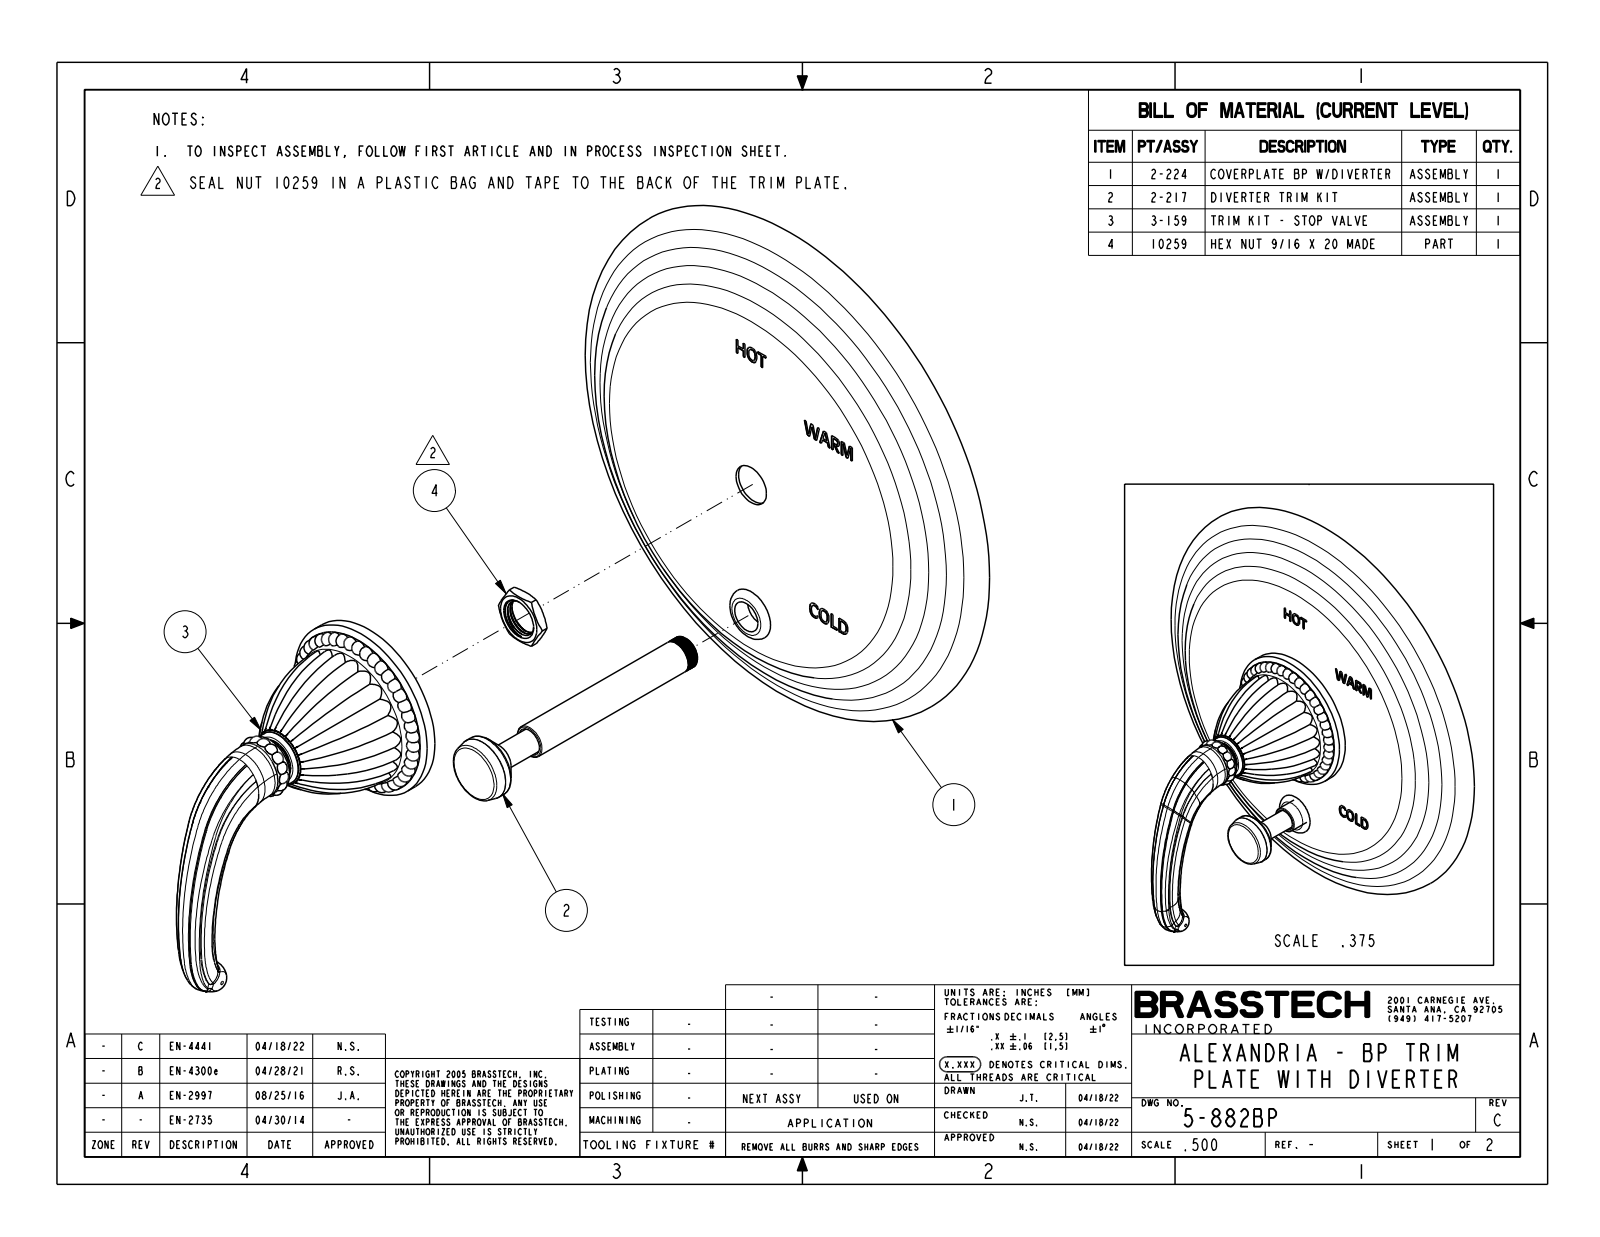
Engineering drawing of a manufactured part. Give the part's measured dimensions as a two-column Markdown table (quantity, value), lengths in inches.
| quantity | value |
| --- | --- |
| part name | 5-882BP |
| STEP written by | CREO PARAMETRIC BY PTC INC, 2018400 (CONFIG_CONTROL_DESIGN) |
| units | inches |
| bodies | 1 solid, 755 faces (132 planar, 16 cylindrical, 607 other) |
| overall size | 7.75 × 7.75 × 4.367 |
| volume | 33.84 in³ |
| surface area | 121.1 in² |
| round bosses / shafts (diameter × count) | 2.57 × 1, 0.9 × 1, 0.787 × 1, 0.775 × 1, 0.472 × 1, 0.4 × 1, 0.354 × 1 |
| main face-to-face distances | 0.754, 2.106, 1.352, 2.564, 1.81, 0.458, 0.75, 1.356, 1.814, 2.595 |
